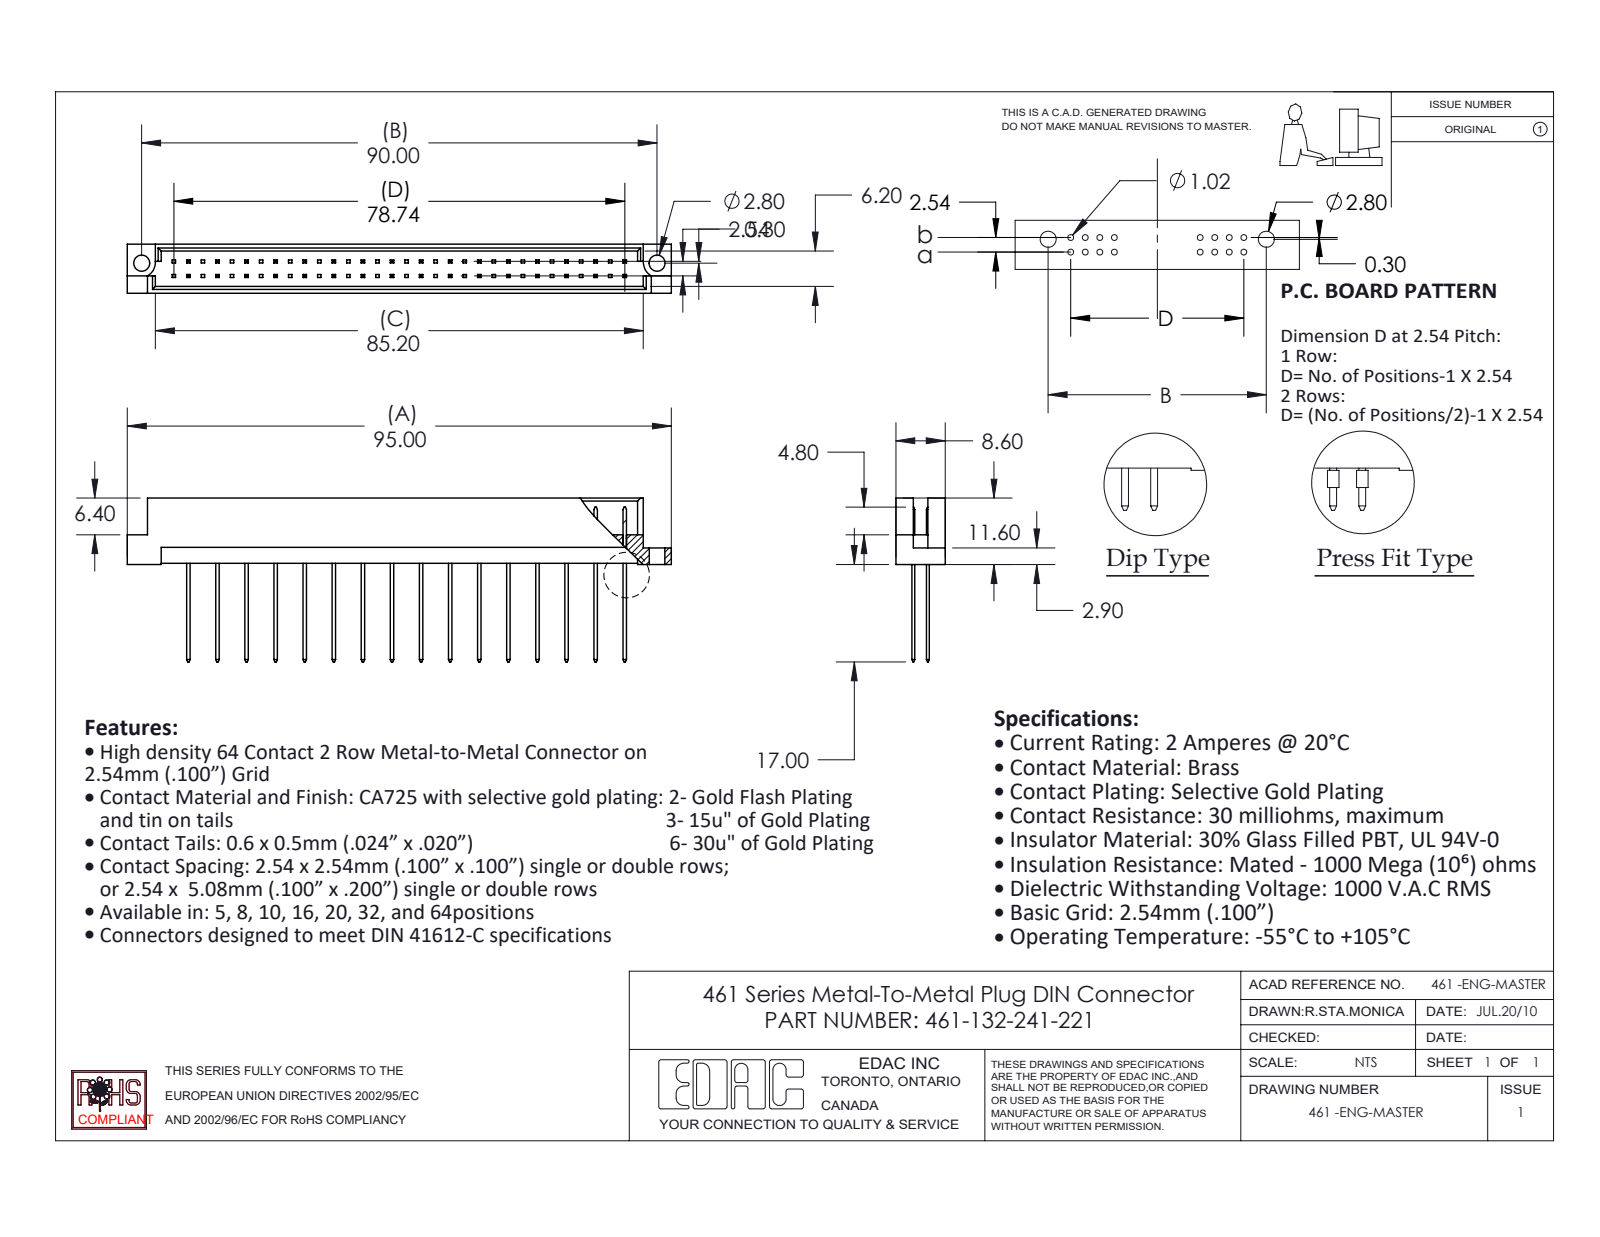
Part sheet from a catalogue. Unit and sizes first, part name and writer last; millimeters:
Units: millimetres
Overall size (bounding box): 95 × 28.6 × 8.6
Round holes (diameter × count): ⌀2.8 ×2
Partial cylindrical surfaces — rounded edges, fillets, slot ends (radius × count): R2.8 ×2
Main face-to-face distances: 1.2, 7.4, 8.6, 6.2, 2.54, 3.28, 5.32, 2.08, 4.12, 2.78
Hole centre spacings: 90
Volume: 4 912 mm³ · Surface area: 7 560 mm²
Bodies: 33 solids, 753 faces (746 planar, 7 cylindrical, 0 other)
Part name (STEP PRODUCT): 461-290_41; 461 Part_64; 461-132-241-221
STEP written by: SolidWorks 2020 (CONFIG_CONTROL_DESIGN)
